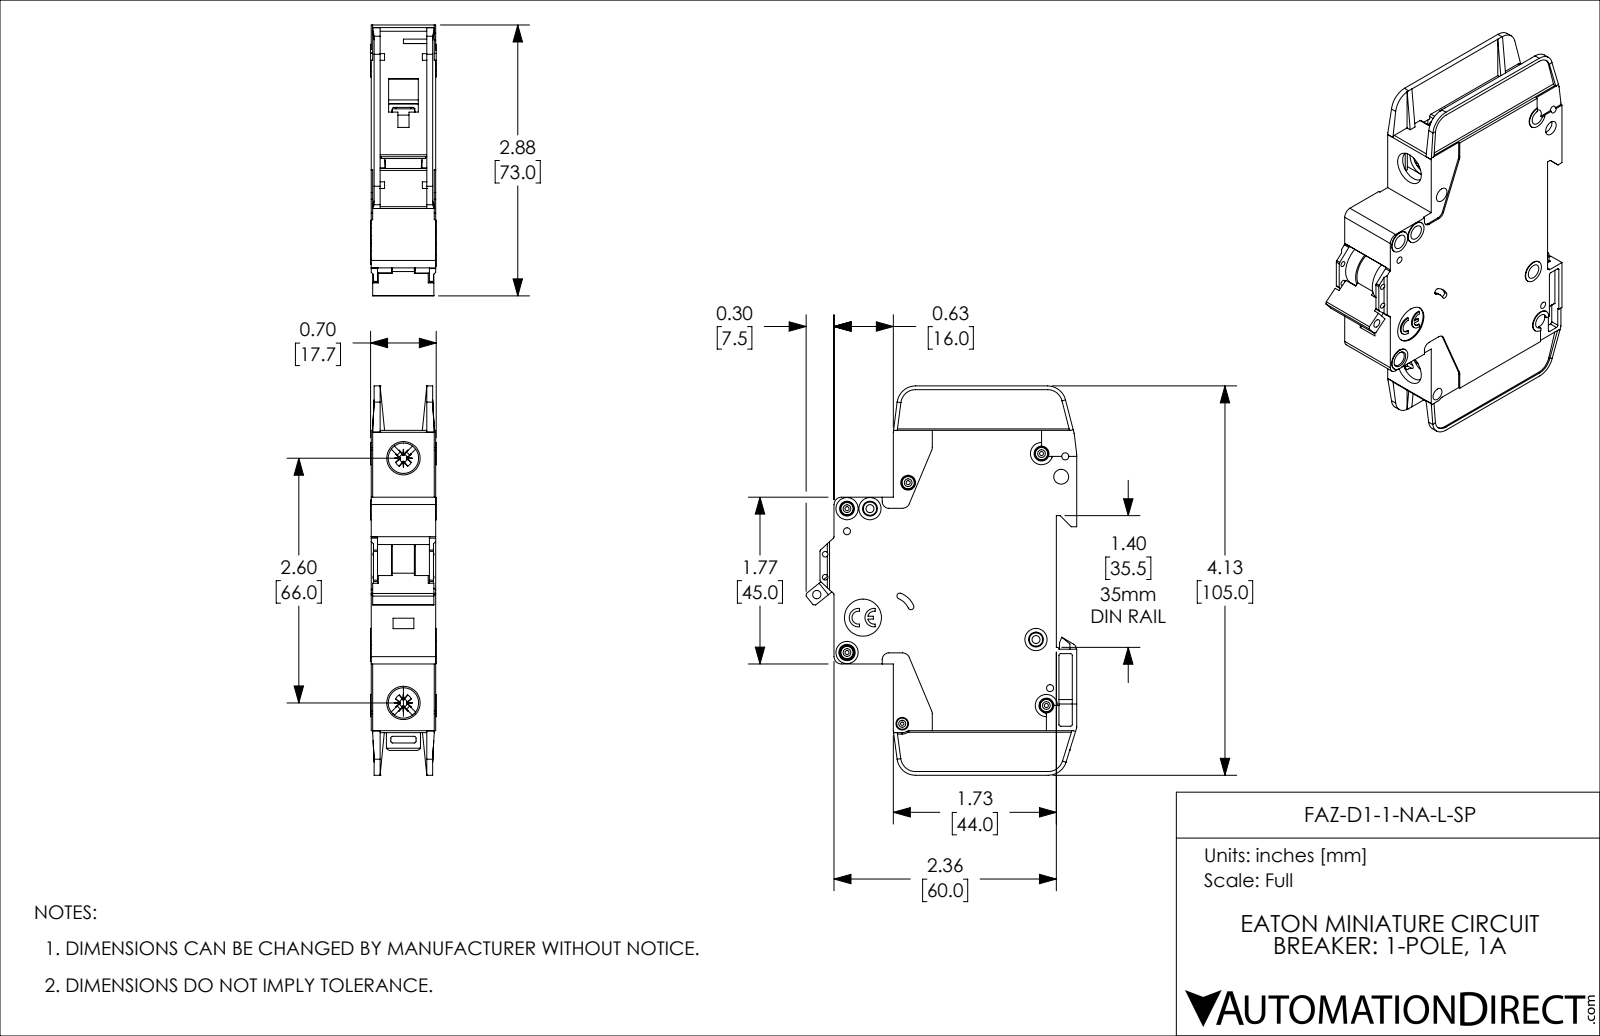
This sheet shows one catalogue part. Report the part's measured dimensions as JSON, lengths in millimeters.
{"part_name": "FAZ-D1-1-NA-L-SP", "step_written_by": "SolidWorks 2019 (AUTOMOTIVE_DESIGN)", "units": "millimeters", "bodies": {"solids": 1, "faces": 1127, "planar": 671, "cylindrical": 357, "other": 99}, "overall_size": [105, 73.1, 17.7], "volume_mm3": 76720, "surface_area_mm2": 26460, "round_holes": [[4, 8], [1.1, 5], [1.9, 4], [1.5, 2], [2.2, 2], [8.2, 2], [0.9, 1], [2.3, 1], [2.5, 1], [3.4, 1], [10, 1]], "round_bosses_or_shafts": [[3.3, 5], [6, 4], [3, 2], [2.5, 1]], "partial_cylinders_radius": [[0.5, 42], [0.4, 10], [1, 10], [2, 8], [5, 5], [0.2, 4], [0.7, 4], [1.1, 4]], "face_to_face_distances": [1.2, 17.4, 15, 16.2, 2.4, 13.8, 0.4, 0.8, 12.6, 14.6], "hole_center_spacings": [6.2, 13.6, 22.1, 4.8, 5.1, 5.2, 5.6, 6.1]}
